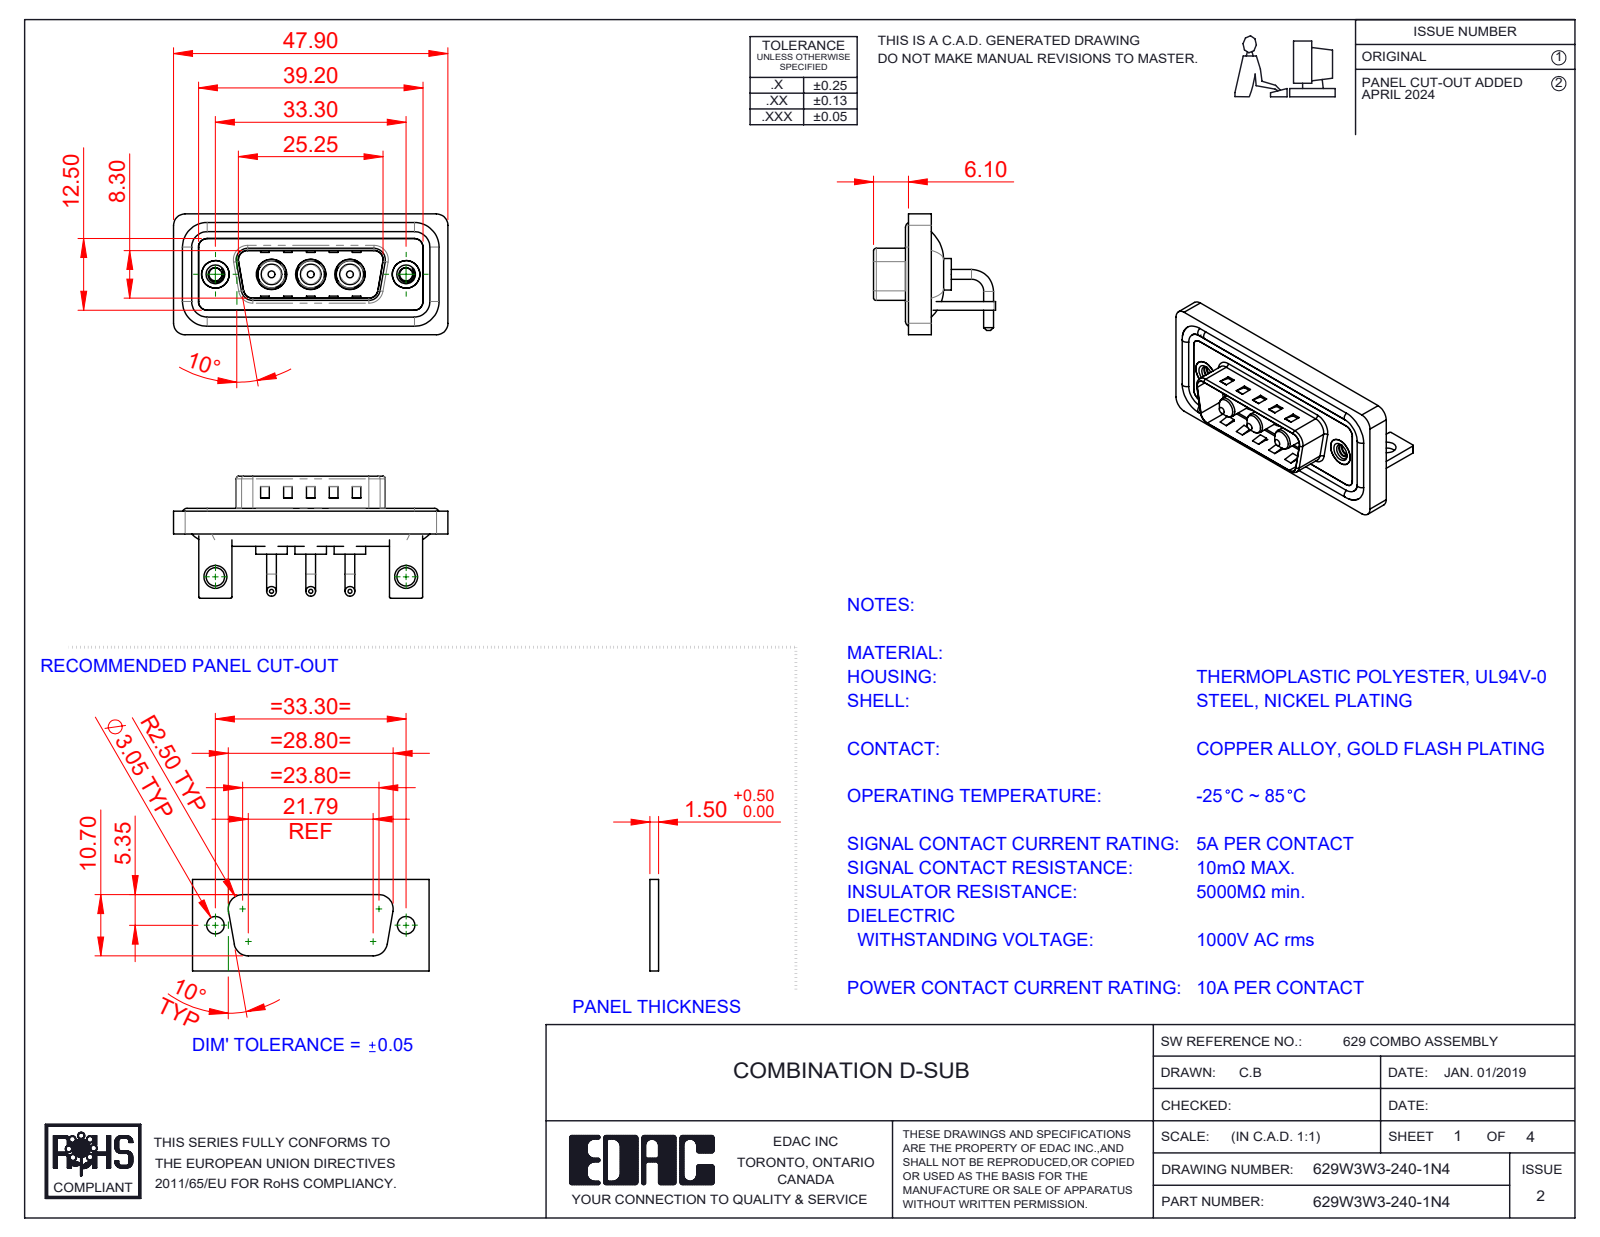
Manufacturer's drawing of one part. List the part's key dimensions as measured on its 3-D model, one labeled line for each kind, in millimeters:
Part name (STEP PRODUCT): 629Combo Threaded Rivet_3; 629Combo Housing_3W3; Power Pin_10A RA; 629Combo Shell Rear_15 Contacts (+4 more)
STEP written by: SolidWorks 2023 (CONFIG_CONTROL_DESIGN)
Units: millimetres
Bodies: 15 solids, 616 faces (227 planar, 265 cylindrical, 124 other)
Overall size (bounding box): 47.9 × 21.3 × 21.1
Volume: 5 882 mm³ · Surface area: 9 470 mm²
Round holes (diameter × count): ⌀4.85 ×3, ⌀5.3 ×3, ⌀2.26 ×2, ⌀3.2 ×2, ⌀4 ×2, ⌀4.8 ×2, ⌀5 ×2
Round bosses / shafts (diameter × count): ⌀1.7 ×6, ⌀1.6 ×4, ⌀5.5 ×3, ⌀5.2 ×3, ⌀4.75 ×3, ⌀3.75 ×3, ⌀3.6 ×3, ⌀4.9 ×2
Partial cylindrical surfaces — rounded edges, fillets, slot ends (radius × count): R2 ×21, R1.5 ×18, R0.25 ×16, R0.5 ×9, R1.6 ×8, R0.6 ×4, R0.65 ×4, R0.9 ×4
Main face-to-face distances: 0.4, 1.5, 0.8, 2.9, 1.1, 2.1, 3.7, 1.6, 1.2, 4.5
Hole centre spacings: 6.85, 9.8, 16.65, 23.5, 33.3, 13.7
